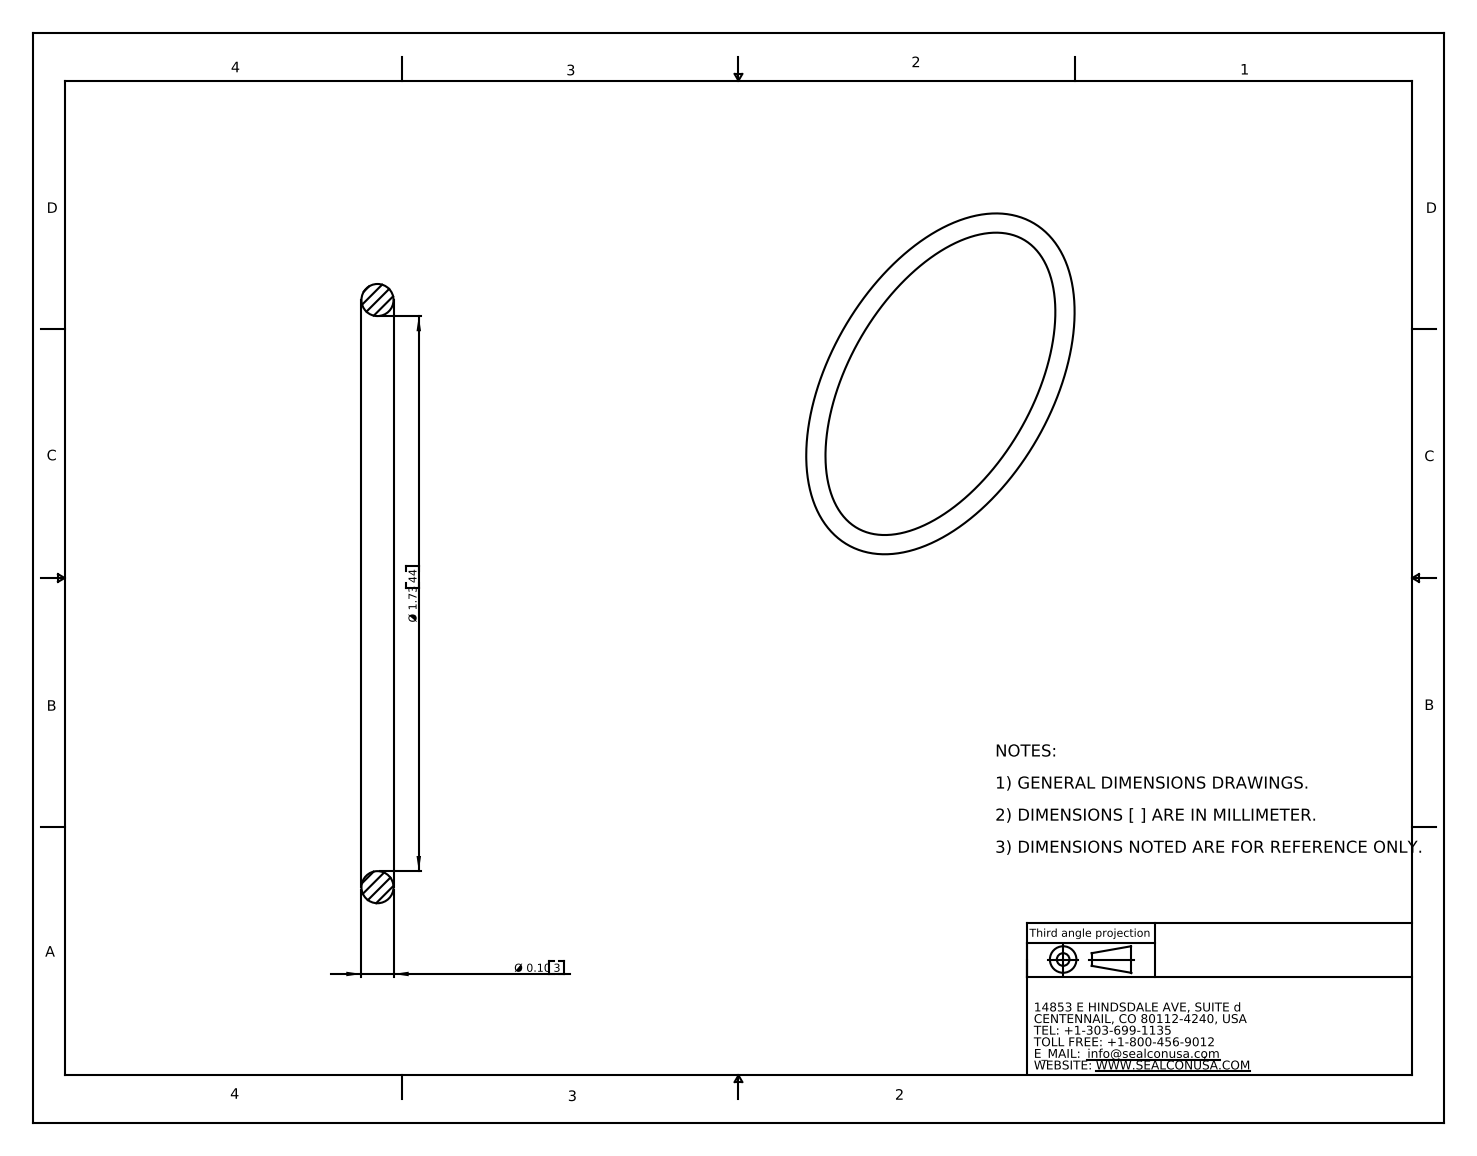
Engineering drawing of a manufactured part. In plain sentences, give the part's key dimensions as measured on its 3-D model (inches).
The part is named "OR-36-BNOR-64-BN". Its 3-D file was written by "SolidWorks 2007 (CONFIG_CONTROL_DESIGN)". It is 1 solid with 4 faces: 0 planar, 0 cylindrical and 4 other. Overall it measures 1.93 by 1.93 by 0.1 inches. Its volume is 0.045 cubic inches and its surface area 1.806 square inches.
